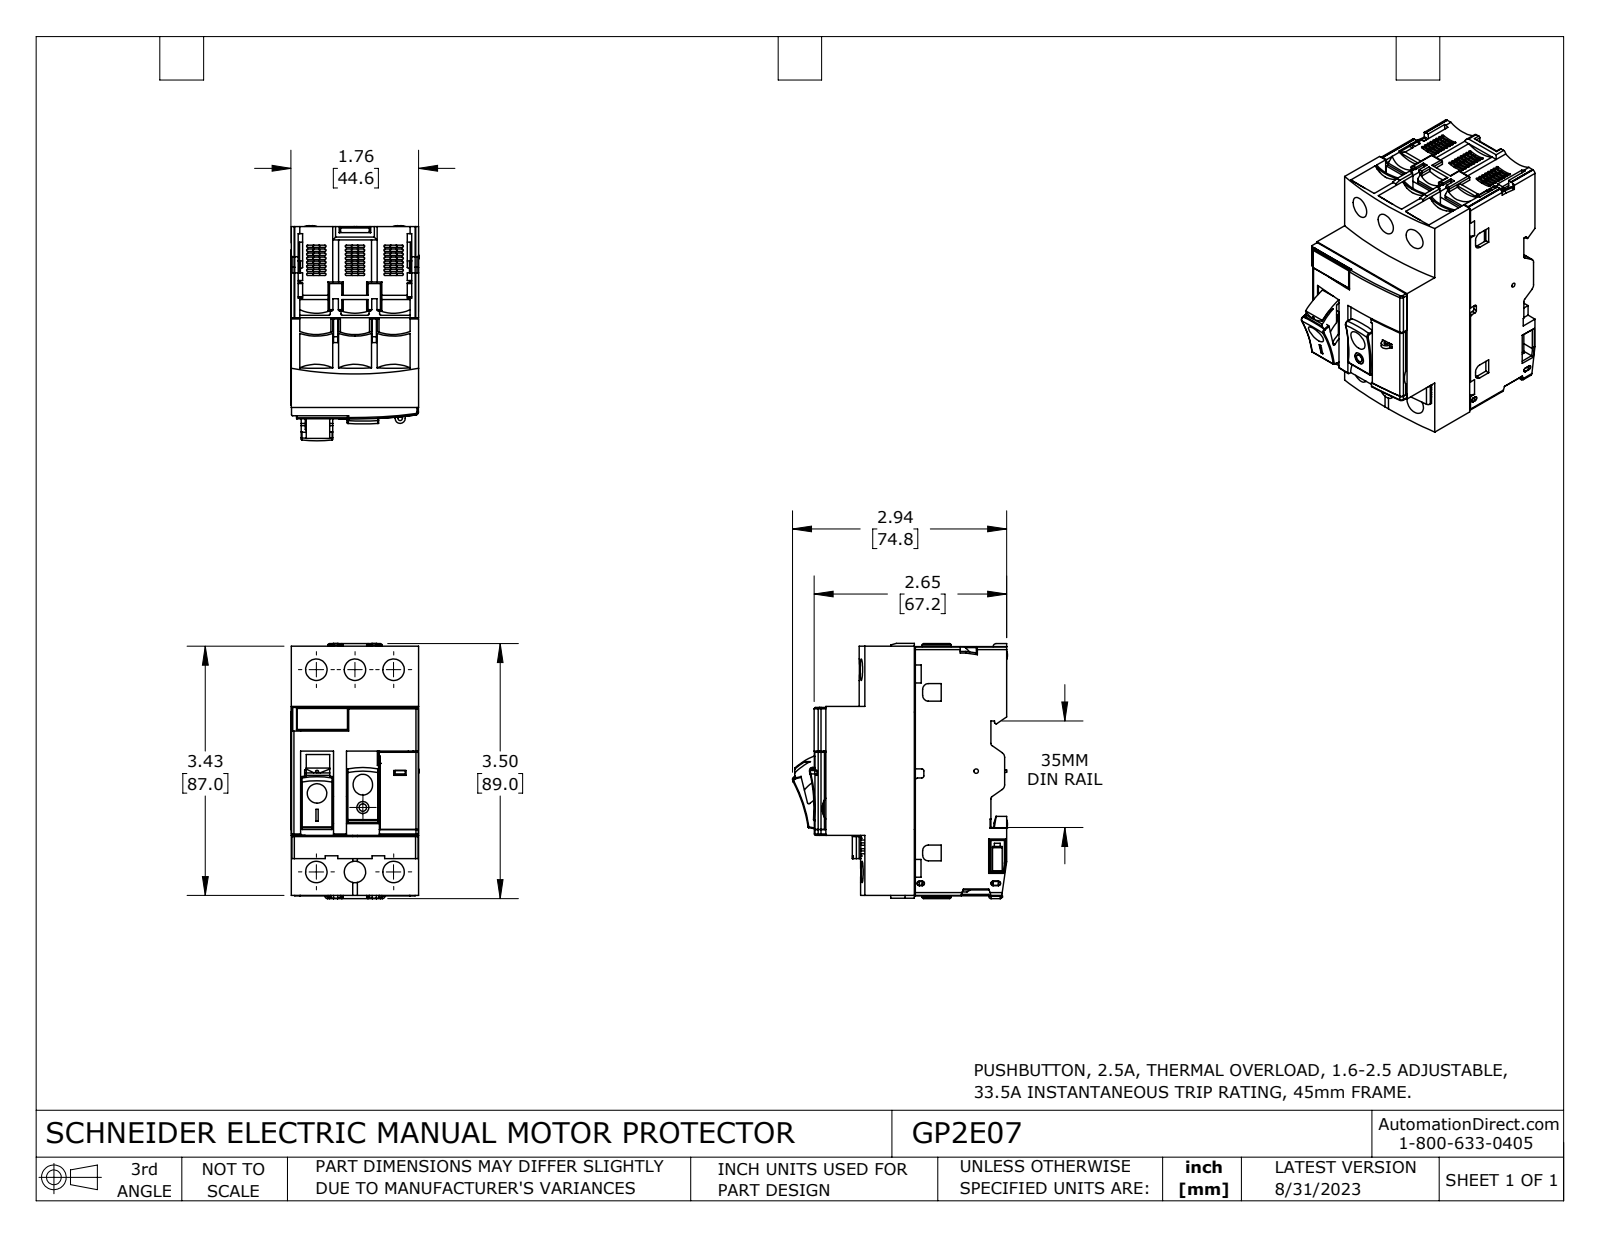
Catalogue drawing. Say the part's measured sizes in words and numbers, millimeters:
The part is named "GP2E07". Its 3-D file was written by "SolidWorks 2021 (CONFIG_CONTROL_DESIGN)". It is 15 solids with 2269 faces: 1521 planar, 657 cylindrical and 91 other. Overall it measures 89.1 by 75.1 by 44.8 millimeters. Its volume is 189 800 cubic millimeters and its surface area 63 830 square millimeters. Round holes: 6 of diameter 7.5, 5 of diameter 5, 2 of diameter 1.5, 1 of diameter 4, 1 of diameter 4.2, 1 of diameter 8, 1 of diameter 8.3, 1 of diameter 8.5, 1 of diameter 8.7. Round bosses or shafts: 2 of diameter 6.2, 2 of diameter 3, 1 of diameter 9.7, 1 of diameter 2.6, 1 of diameter 1.2. Partial cylindrical surfaces (rounded edges, fillets, slot ends): 104 of radius 0.4, 47 of radius 0.5, 16 of radius 1, 12 of radius 0.3, 12 of radius 0.3, 12 of radius 0.8, 8 of radius 1.5, 6 of radius 0.1. The main face-to-face distances are 44.5, 13.5, 2.9, 31.3, 44.6, 1.5, 41.6, 14.8, 26.7, 29.7. The hole center spacings are 13.5, 71.9, 70.6, 8.8, 10.2, 13.9, 17, 18.4.
